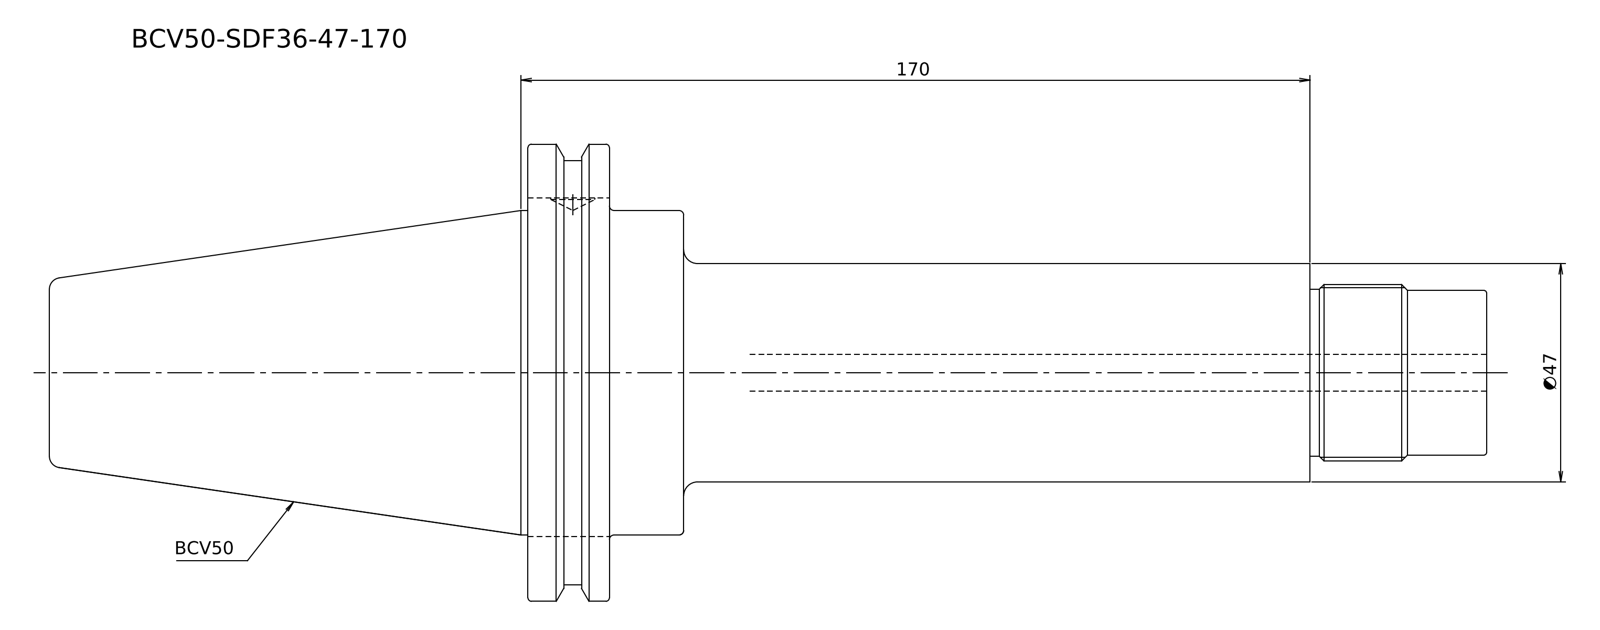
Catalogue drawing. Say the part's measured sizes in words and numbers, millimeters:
Its 3-D file was written by "Kubotek KeyCreator 2011 V10.0.2 (22737) (automotive_design)". It is 1 solid with 17 faces: 7 planar, 6 cylindrical and 4 other. Overall it measures 271.6 by 98.42 by 98.42 millimeters. Its volume is 677 493 cubic millimeters and its surface area 60 658 square millimeters. Round bosses or shafts: 1 of diameter 98.42, 1 of diameter 91.29, 1 of diameter 69.85, 1 of diameter 47. The main face-to-face distances are 17.55, 150.95, 168.5, 134.95, 16, 33.55, 271.6, 136.65, 120.65, 103.1.
